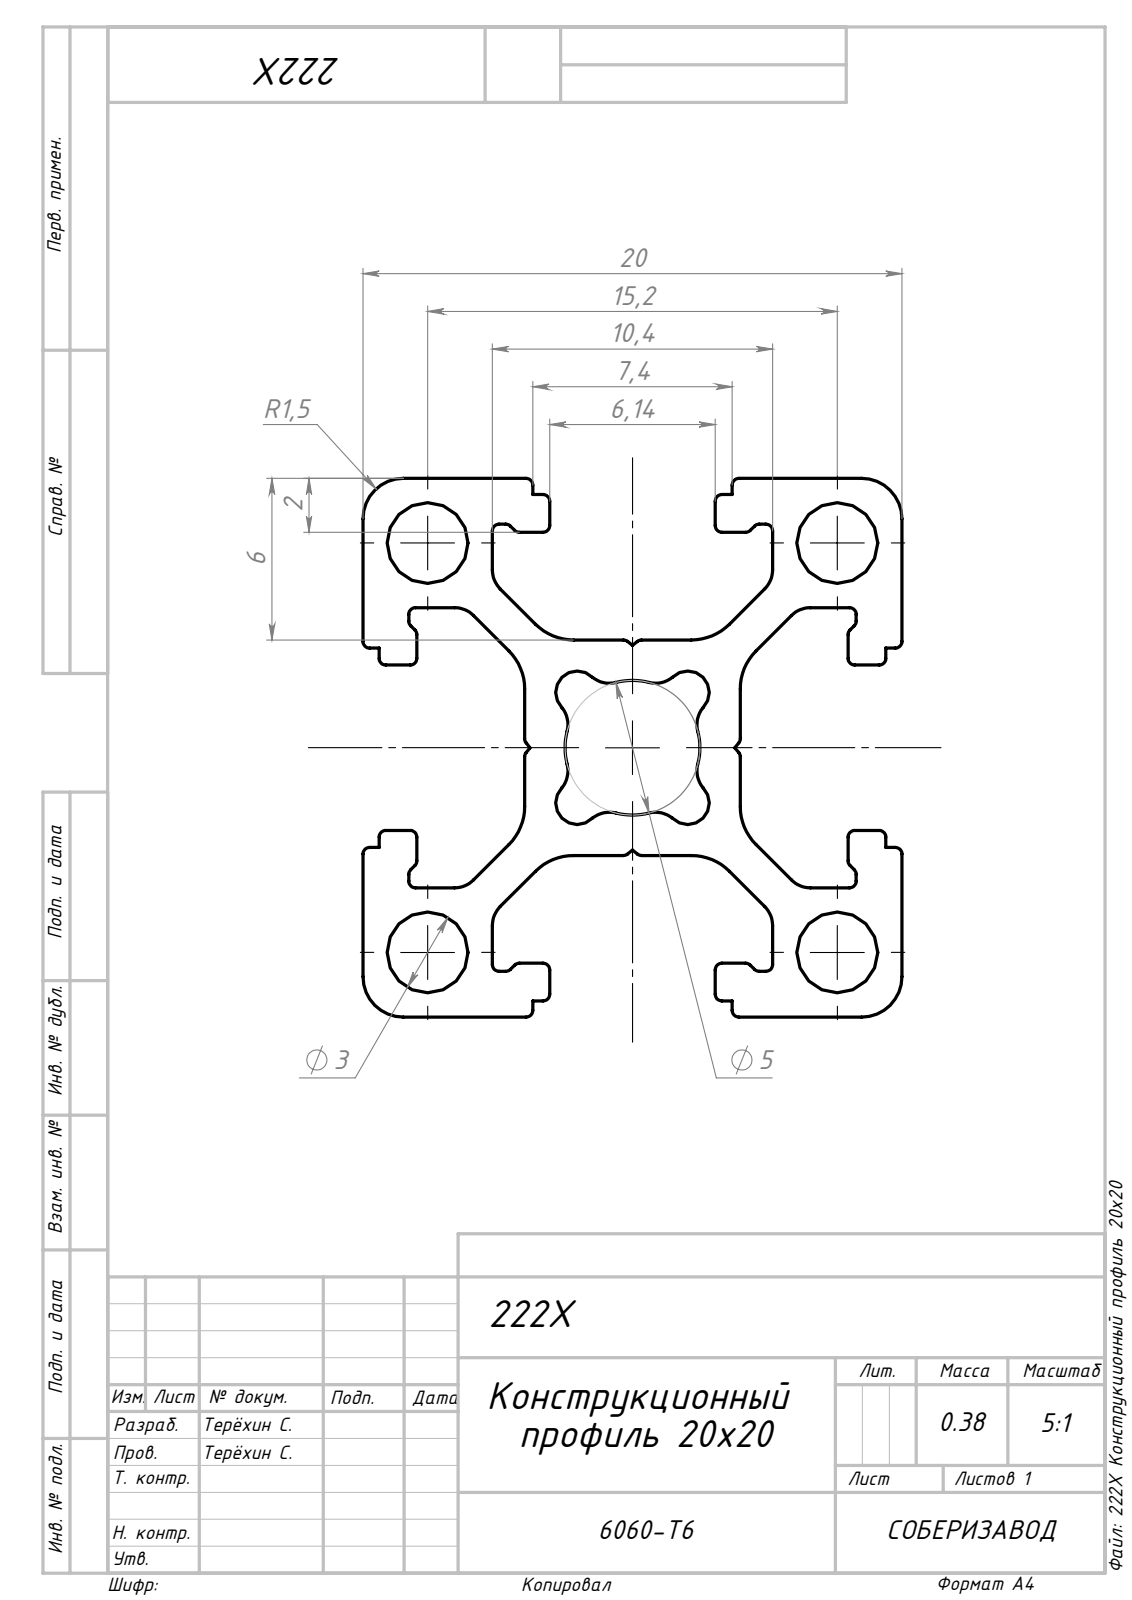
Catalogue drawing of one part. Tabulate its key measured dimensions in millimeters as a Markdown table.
| quantity | value |
| --- | --- |
| part name | 222 Конструкционный профиль 20х20_00; Сборка1 |
| STEP written by | SolidWorks 2022 (AUTOMOTIVE_DESIGN) |
| units | millimeters |
| bodies | 1 solid, 195 faces (90 planar, 105 cylindrical, 0 other) |
| overall size | 1000 × 20 × 20 |
| volume | 142 104 mm³ |
| surface area | 208 901 mm² |
| round holes (diameter × count) | 3 × 4 |
| partial cylindrical surfaces (radius × count) | 0.25 × 56, 1 × 16, 2 × 8, 0.8 × 4, 1.5 × 4, 2.5 × 1 |
| main face-to-face distances | 20, 6, 14, 4.8, 15.2, 1.2, 9.2, 1.4, 12, 8 |
| hole center spacings | 15.2, 21.5 |
